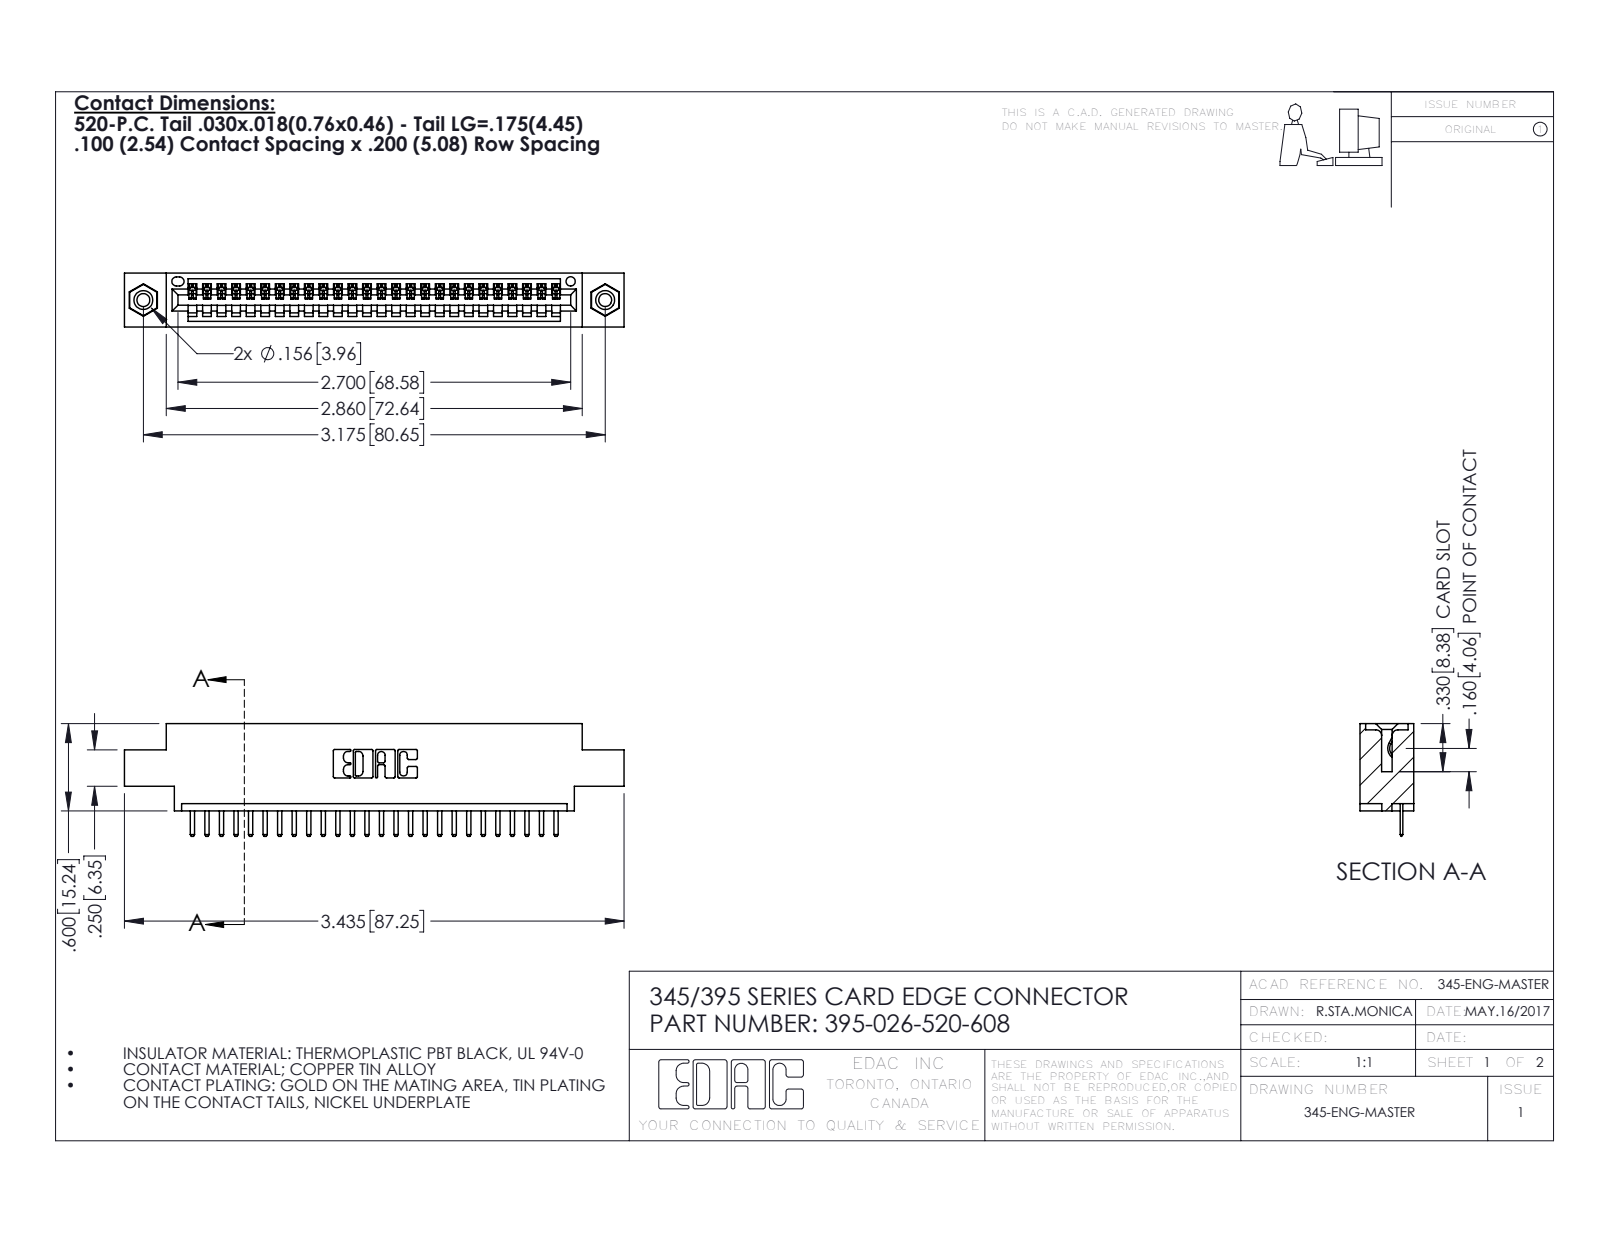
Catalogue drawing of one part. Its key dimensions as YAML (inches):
part_name: "395-026-520-608; 345-292-001_345-293-120; 345 Part_0.170 Offset - 0.156 Dia-TI; 345-250-001_345-250-003-102"
step_written_by: "SolidWorks 2016 (CONFIG_CONTROL_DESIGN)"
units: inches
bodies: {solids: 29, faces: 1802, planar: 1208, cylindrical: 578, other: 16}
overall_size: [3.435, 0.775, 0.37]
volume: 0.486
surface_area: 15.91
round_holes:
  - {diameter: 0.089, count: 2}
  - {diameter: 0.125, count: 2}
  - {diameter: 0.156, count: 2}
  - {diameter: 0.064, count: 1}
round_bosses_or_shafts:
  - {diameter: 0.155, count: 2}
partial_cylinders:
  - {radius: 0.01, count: 54}
  - {radius: 0.006, count: 52}
  - {radius: 0.01, count: 22}
  - {radius: 0.007, count: 6}
  - {radius: 0.031, count: 6}
  - {radius: 0.026, count: 3}
  - {radius: 0.031, count: 2}
  - {radius: 0.04, count: 2}
face_to_face_distances: [0.072, 0.298, 0.37, 0.2, 0.098, 0.272, 0.025, 0.225, 0.072, 0.175]
hole_center_spacings: [0.27, 2.94, 3.175]
